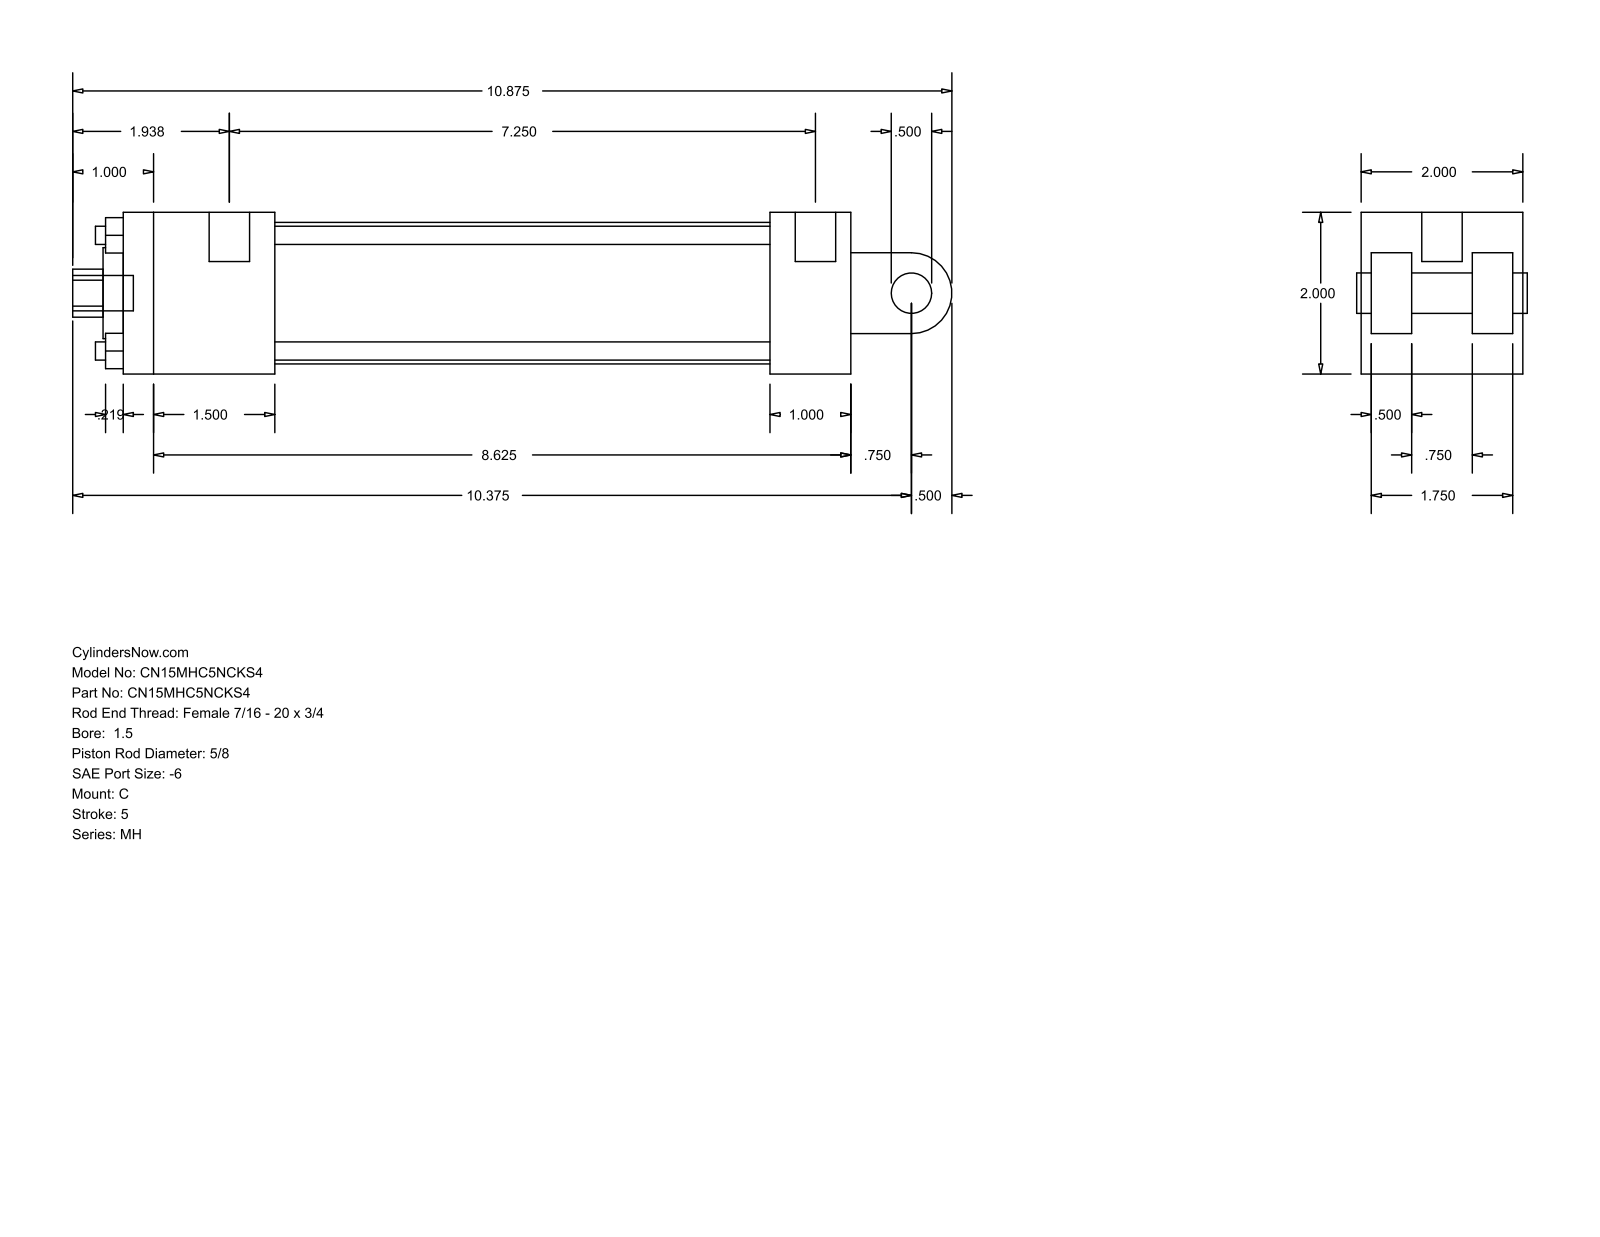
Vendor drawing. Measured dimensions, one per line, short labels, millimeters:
name: MH_C__0150_0.625
written by: GSSL Pune (CONFIG_CONTROL_DESIGN)
unit: mm
bodies: 0 solids, 99 faces (70 planar, 29 cylindrical, 0 other)
size: 276.23 × 50.8 × 50.8
holes: 4× ⌀5.71, 2× ⌀5.56, 1× ⌀12.7, 1× ⌀15.88, 1× ⌀28.57, 1× ⌀44.45
bosses: 2× ⌀12.7, 2× ⌀5.56, 1× ⌀11.11
rounds: 1× R7.54, 1× R12.7
face distances: 50.8, 12.7, 228.59, 25.4, 3.17, 15.87, 34.93, 47.63, 31.76, 38.1
hole spacings: 25.68, 36.32, 51.36
